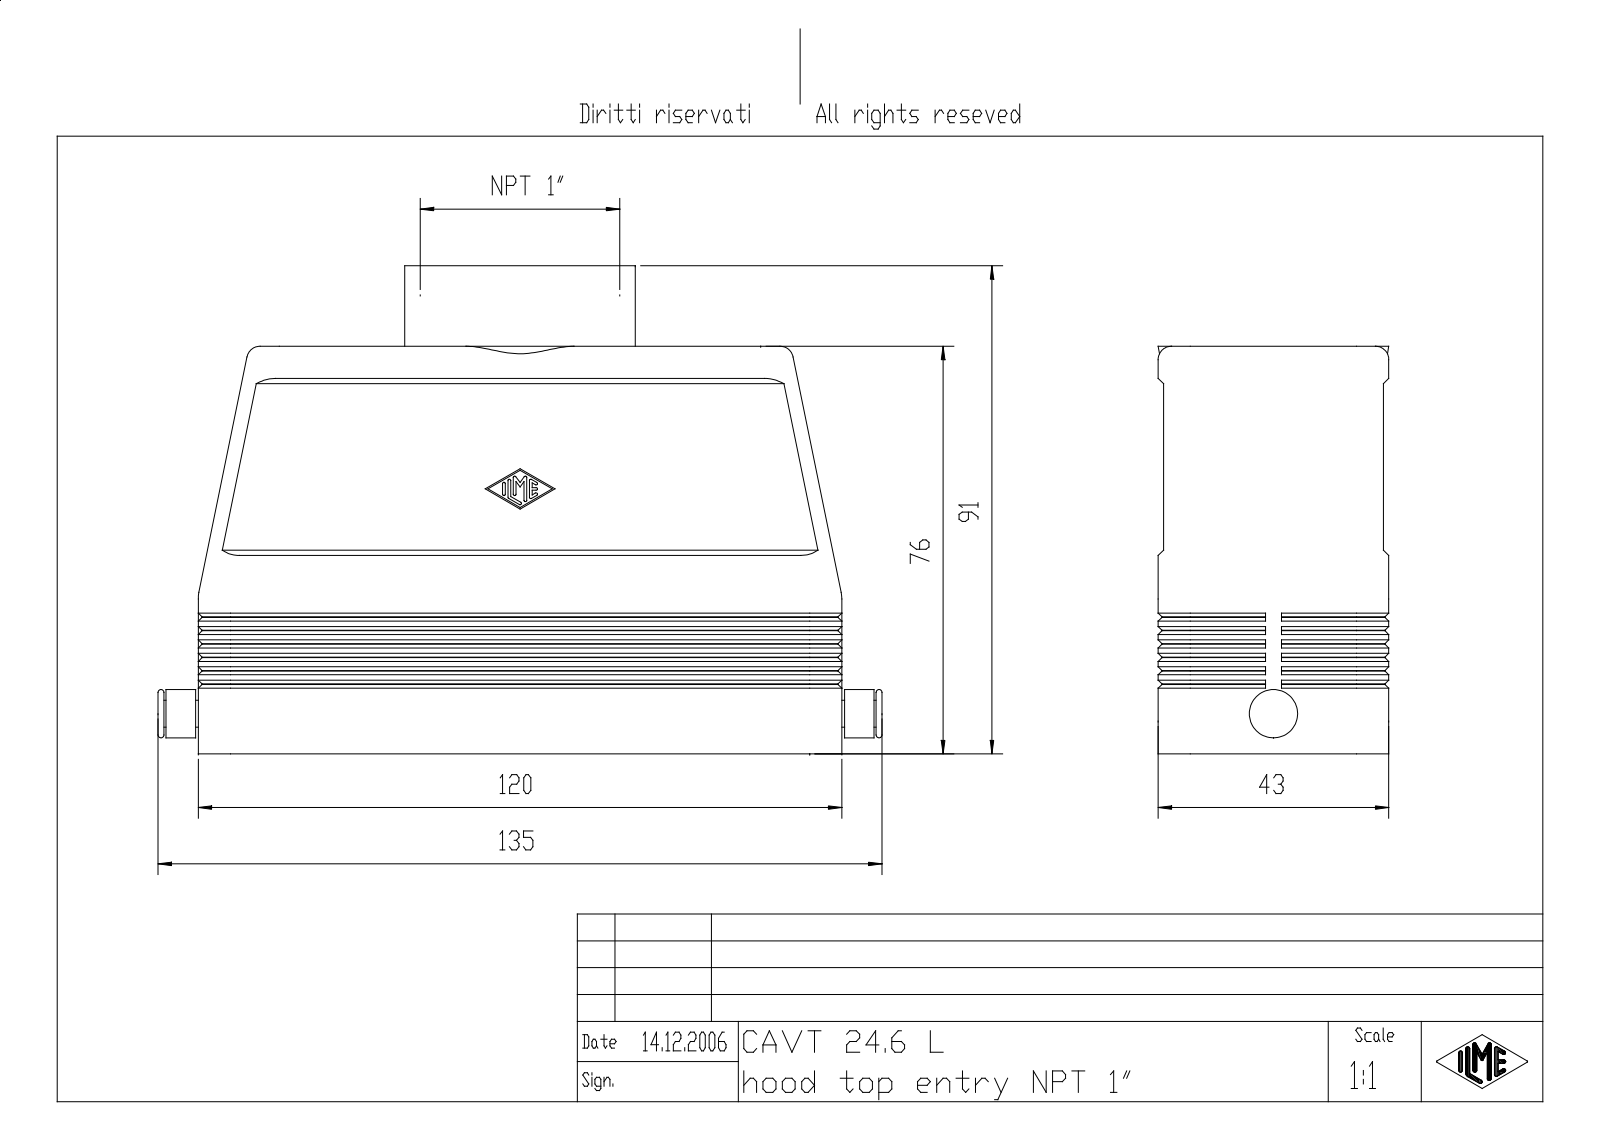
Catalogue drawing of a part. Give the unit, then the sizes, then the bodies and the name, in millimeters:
Units: millimetres
Overall size (bounding box): 135 × 91 × 43
Round holes (diameter × count): ⌀4 ×4, ⌀2.46 ×3, ⌀2.46 ×1
Round bosses / shafts (diameter × count): ⌀43 ×1, ⌀9 ×1, ⌀5 ×1
Partial cylindrical surfaces — rounded edges, fillets, slot ends (radius × count): R0.25 ×14, R6 ×10, R2 ×4, R2.5 ×4, R3 ×4, R5.3 ×4
Main face-to-face distances: 3, 37, 40, 2, 1, 42, 39, 43, 41, 9
Hole centre spacings: 27, 104, 107.45
Volume: 94 436 mm³ · Surface area: 57 527 mm²
Bodies: 1 solid, 416 faces (230 planar, 114 cylindrical, 72 other)
Part name (STEP PRODUCT): MSBO8641
STEP written by: Creo Elements/Direct Modeling 18.0B 02-Dec-2011 (C) Parametric Technology GmbH (AUTOMOTIVE_DESIGN)
